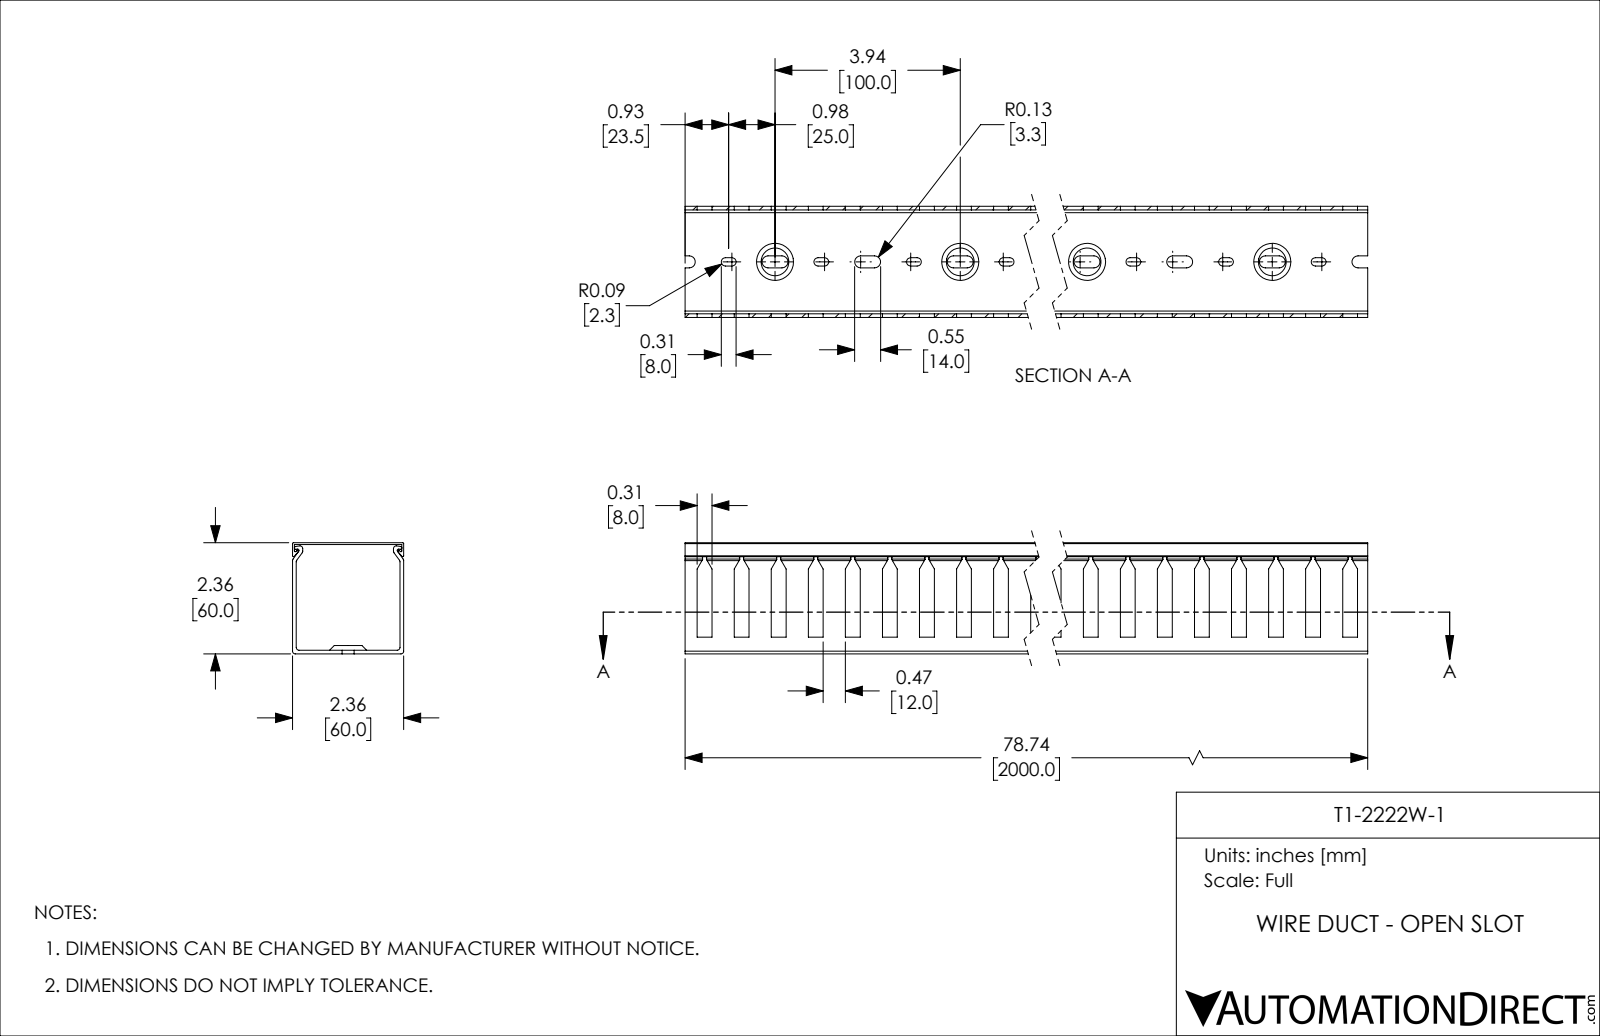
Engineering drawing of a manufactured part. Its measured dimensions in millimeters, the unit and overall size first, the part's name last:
Units: millimetres
Overall size (bounding box): 2000 × 60 × 60
Partial cylindrical surfaces — rounded edges, fillets, slot ends (radius × count): R2.25 ×80, R3.25 ×80, R1.5 ×12, R0.5 ×8, R0.75 ×6
Main face-to-face distances: 2, 58, 60, 1, 59, 57, 56, 4.5, 54.5, 5.5
Volume: 854 712 mm³ · Surface area: 1 012 000 mm²
Bodies: 2 solids, 1005 faces (534 planar, 431 cylindrical, 40 other)
Part name (STEP PRODUCT): T1-2222W-1
STEP written by: SolidWorks 2021 (CONFIG_CONTROL_DESIGN)
